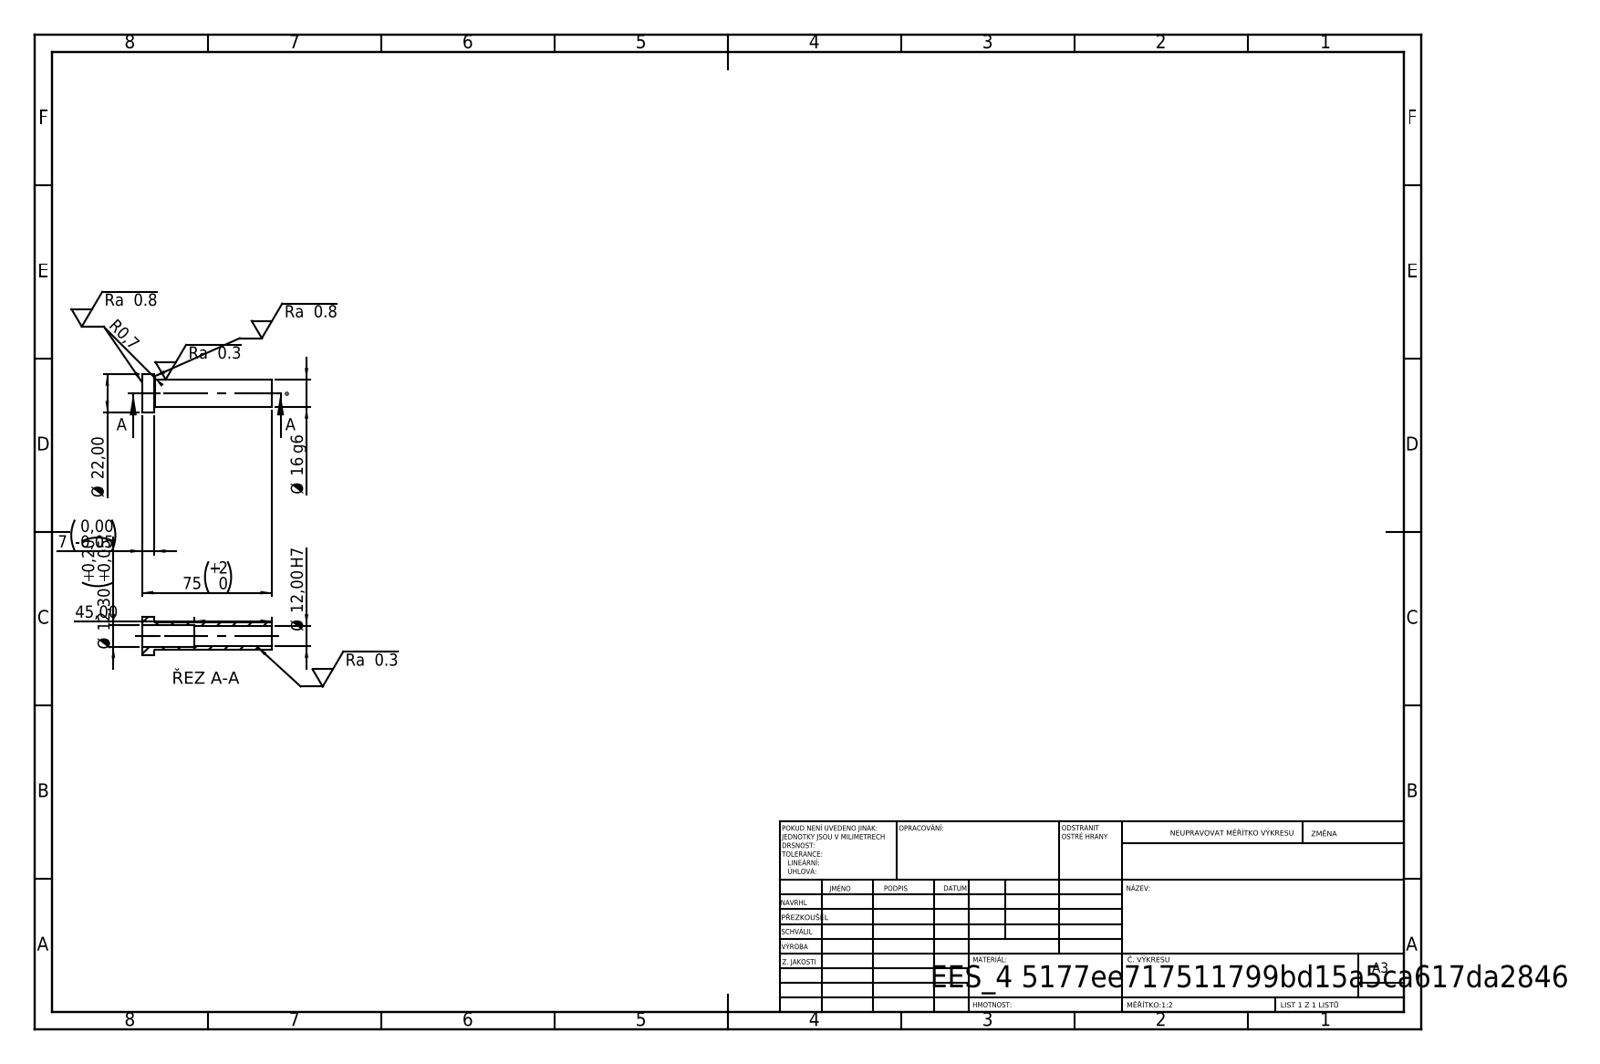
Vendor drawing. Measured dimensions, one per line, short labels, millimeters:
written by: SolidWorks 2019 (CONFIG_CONTROL_DESIGN)
unit: mm
bodies: 1 solid, 14 faces (4 planar, 8 cylindrical, 2 other)
size: 75 × 22 × 22
volume: 7 684 mm³; area: 7 277 mm²
holes: 1× ⌀12, 1× ⌀12.3
bosses: 1× ⌀22, 1× ⌀16
face distances: 7, 75, 68, 30, 23, 45
